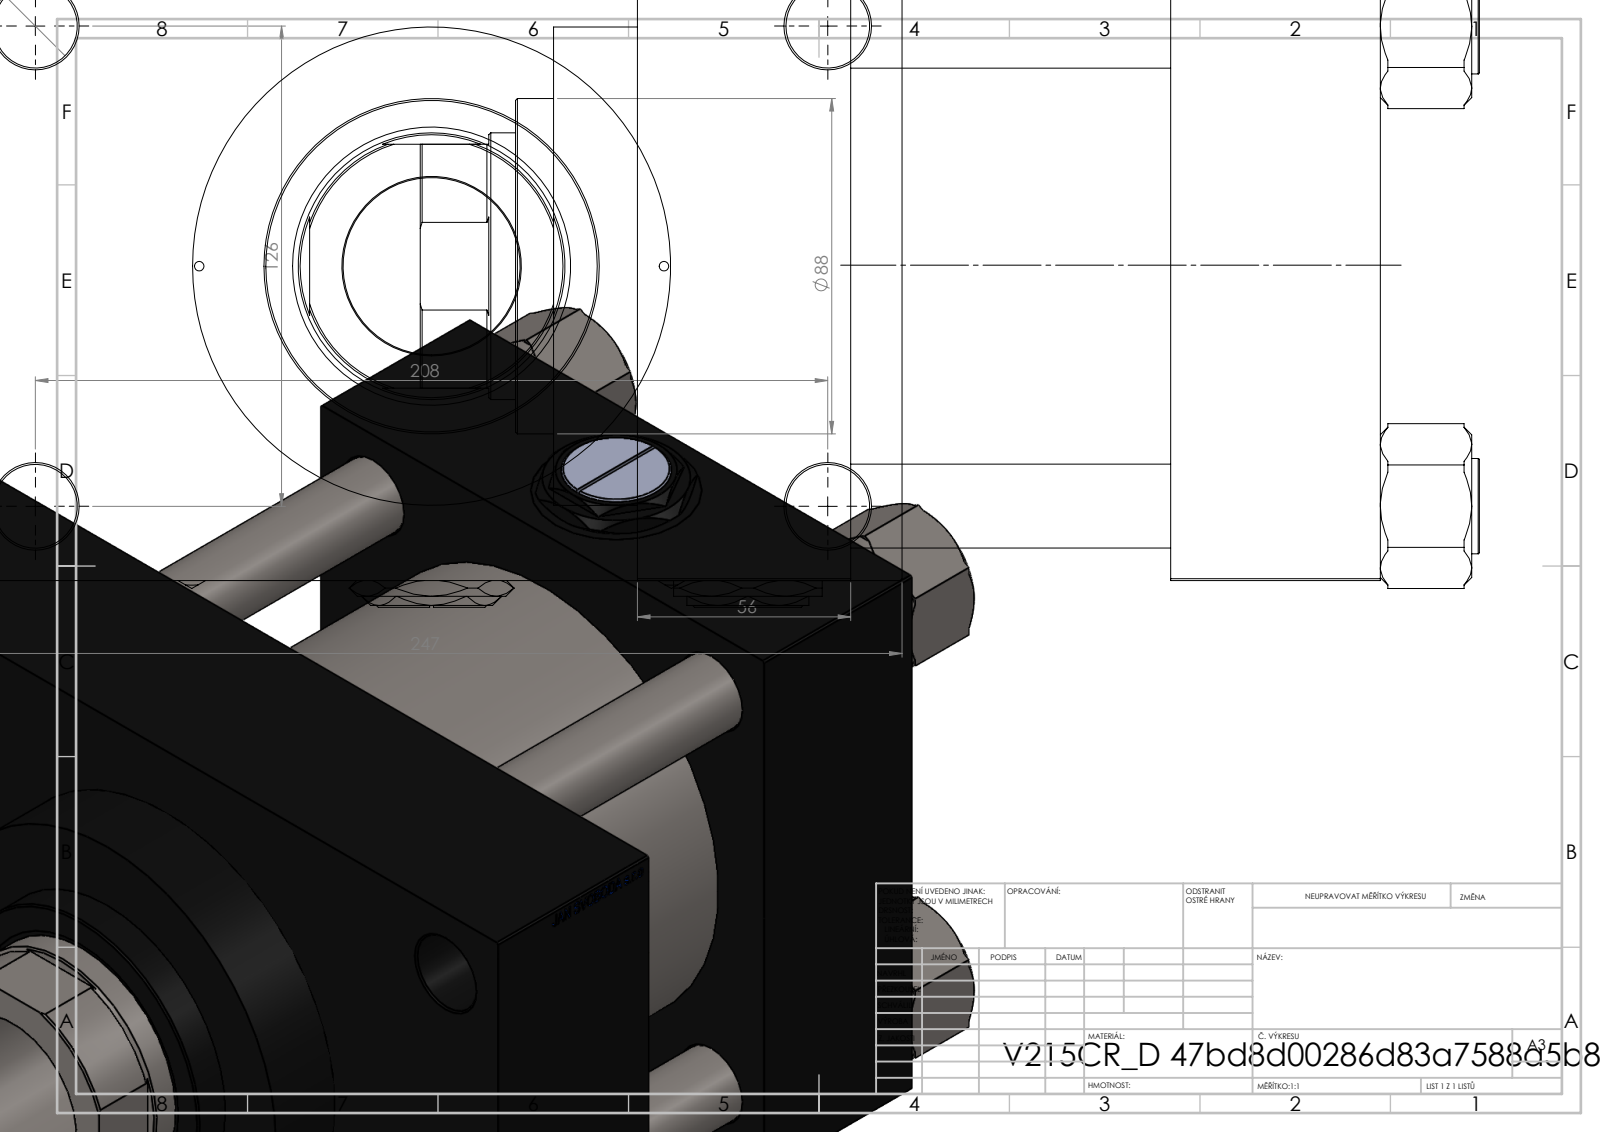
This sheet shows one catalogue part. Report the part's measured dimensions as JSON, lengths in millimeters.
{"part_name": "V215CR_VCP_D; Zatka_pro_OIL_PORT; V215CR_D_Body; NUT_M5_D (+2 more)", "step_written_by": "SolidWorks 2019 (CONFIG_CONTROL_DESIGN)", "units": "millimeters", "bodies": {"solids": 13, "faces": 1239, "planar": 590, "cylindrical": 91, "other": 558}, "overall_size": [278, 247, 179], "volume_mm3": 5062000, "surface_area_mm2": 544772, "round_holes": [[22, 8], [2.5, 2], [7, 2], [32.24, 2], [45, 2], [46.5, 1], [70, 1], [73, 1], [96, 1], [125, 1], [125.5, 1]], "round_bosses_or_shafts": [[25, 4], [131, 1], [88, 1]], "partial_cylinders_radius": [[34, 1]], "face_to_face_distances": [165, 84, 55, 139, 56, 195, 140, 41, 206, 173.74], "hole_center_spacings": [41.05, 62.98, 76.28, 89.02, 121.59, 125.9, 132.47, 139.02]}
